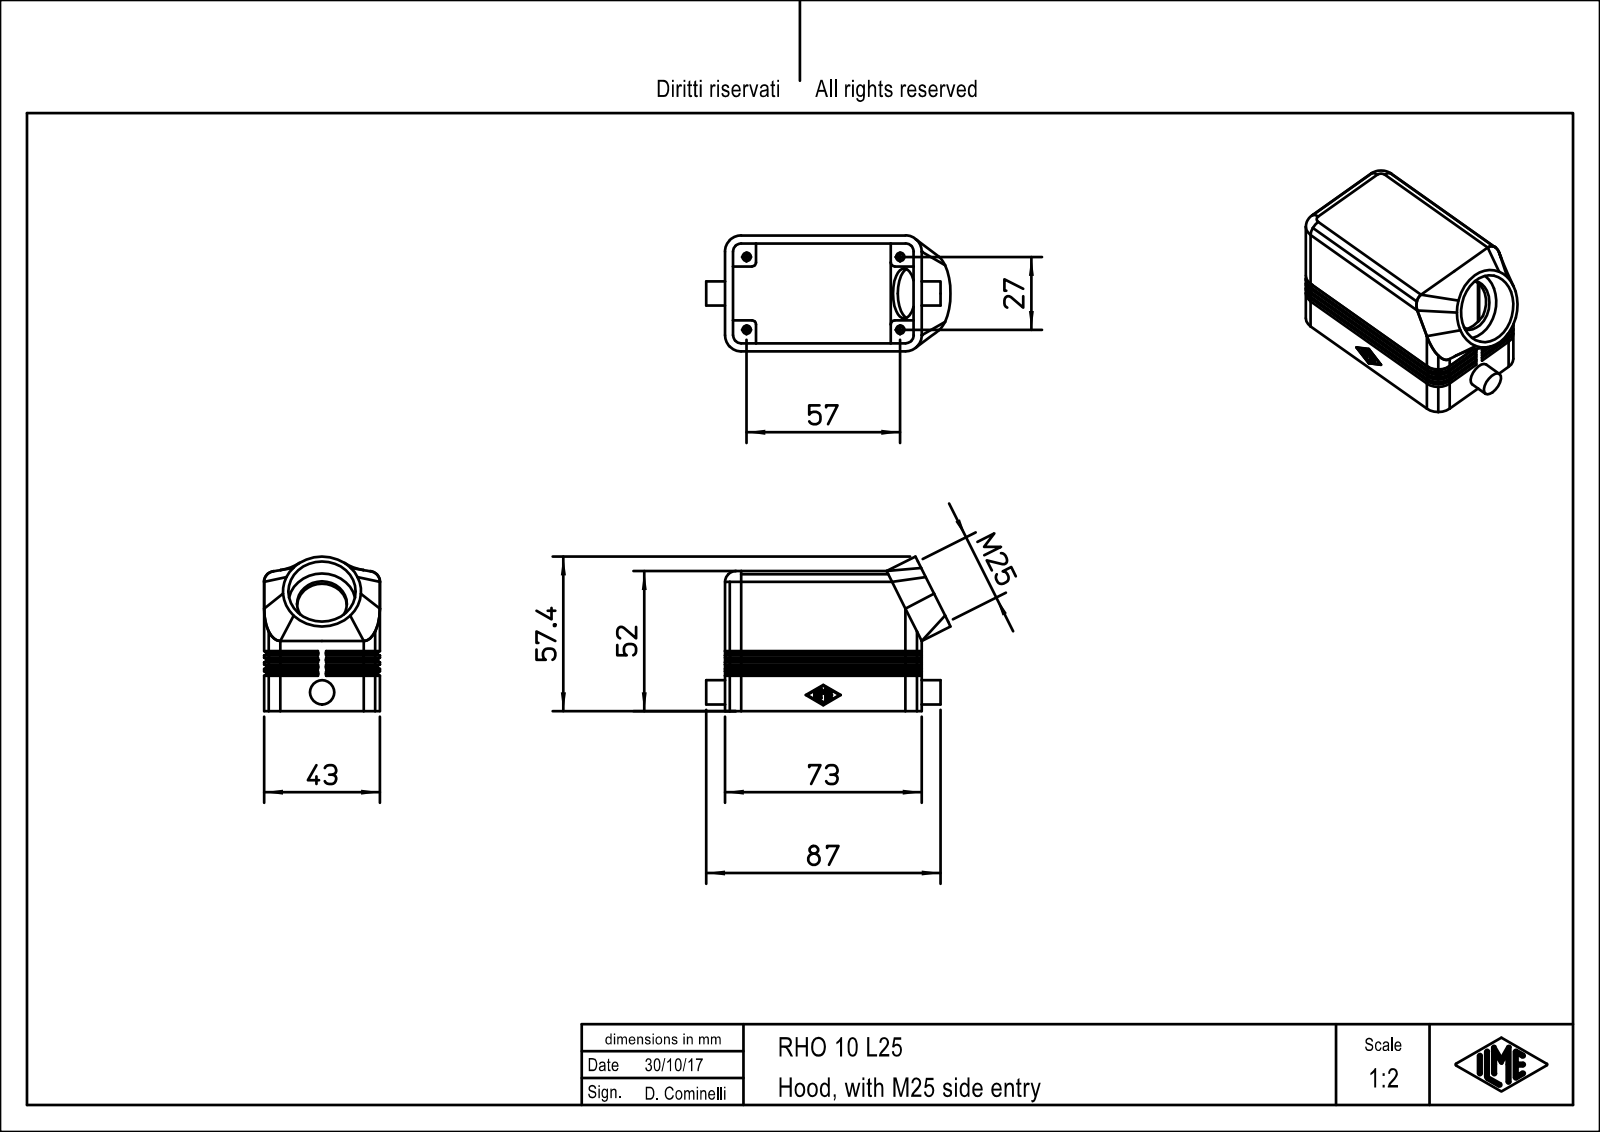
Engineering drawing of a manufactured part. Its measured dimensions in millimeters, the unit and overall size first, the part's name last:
Units: millimetres
Overall size (bounding box): 90.72 × 57.38 × 43
Round holes (diameter × count): ⌀2.46 ×4, ⌀3.1 ×4, ⌀18.5 ×1, ⌀25 ×1
Round bosses / shafts (diameter × count): ⌀9 ×1
Partial cylindrical surfaces — rounded edges, fillets, slot ends (radius × count): R0.4 ×32, R0.25 ×14, R1.5 ×4, R3 ×4, R5 ×4, R6 ×4, R4 ×3
Main face-to-face distances: 3, 40, 43, 37, 8.5, 11.5, 70, 58.5, 61.5, 31.5
Hole centre spacings: 27, 57, 63.07
Volume: 51 083 mm³ · Surface area: 29 527 mm²
Bodies: 1 solid, 460 faces (166 planar, 212 cylindrical, 82 other)
Part name (STEP PRODUCT): RHO_10_L25
STEP written by: PTC Creo Elements/Direct Modeling 19.0E 27-Jun-2016 (C) Parametric Technology GmbH (AUTOMOTIVE_DESIGN)
